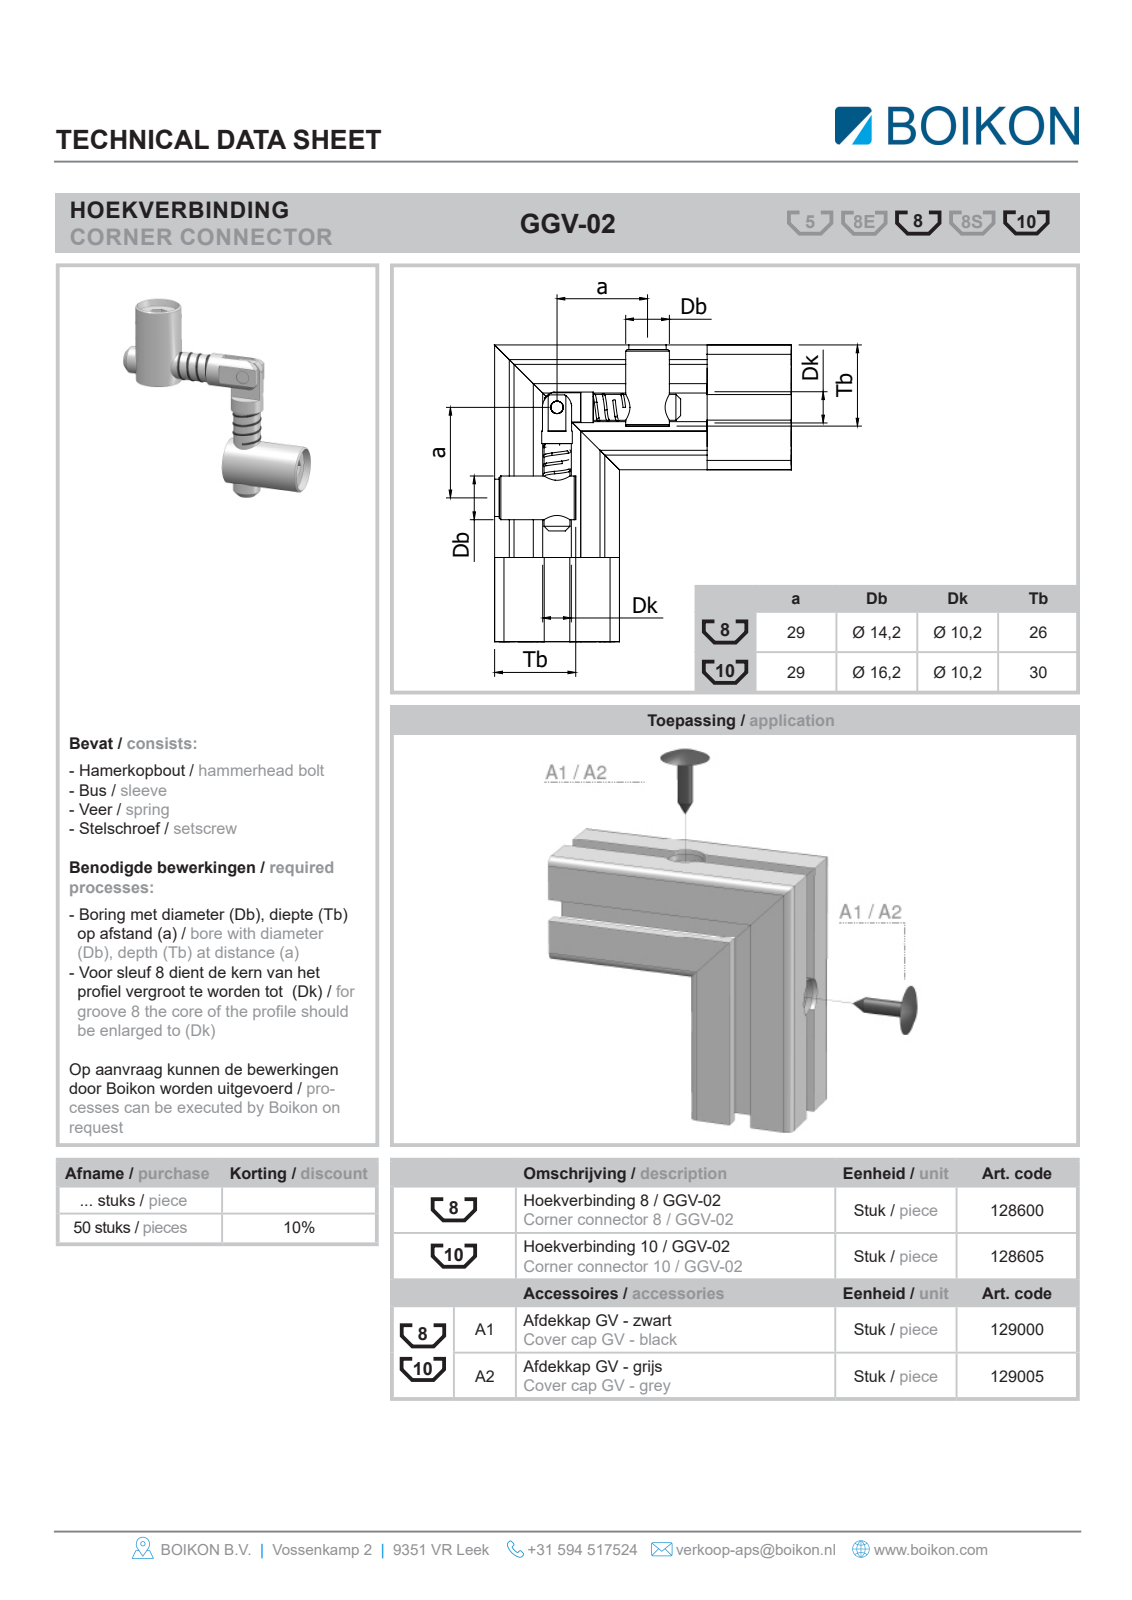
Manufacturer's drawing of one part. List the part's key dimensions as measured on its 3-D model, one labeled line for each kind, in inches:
Part name (STEP PRODUCT): Root; 128605Hoekverbinding 10 / GGV-02BOIKON
STEP written by: HiCAD 2013 1802.4 Build 509 (AUTOMOTIVE_DESIGN)
Units: inches
Bodies: 3 solids, 58 faces (38 planar, 18 cylindrical, 2 other)
Overall size (bounding box): 2.425 × 2.406 × 0.63
Volume: 0.842 in³ · Surface area: 9.179 in²
Round holes (diameter × count): ⌀0.157 ×1
Round bosses / shafts (diameter × count): ⌀0.63 ×2, ⌀0.386 ×2, ⌀0.327 ×2
Partial cylindrical surfaces — rounded edges, fillets, slot ends (radius × count): R0.185 ×1, R0.197 ×1
Main face-to-face distances: 1.142, 0.116, 0.236, 0.098, 0.1, 0.215, 0.217, 0.114, 0.118, 0.315
